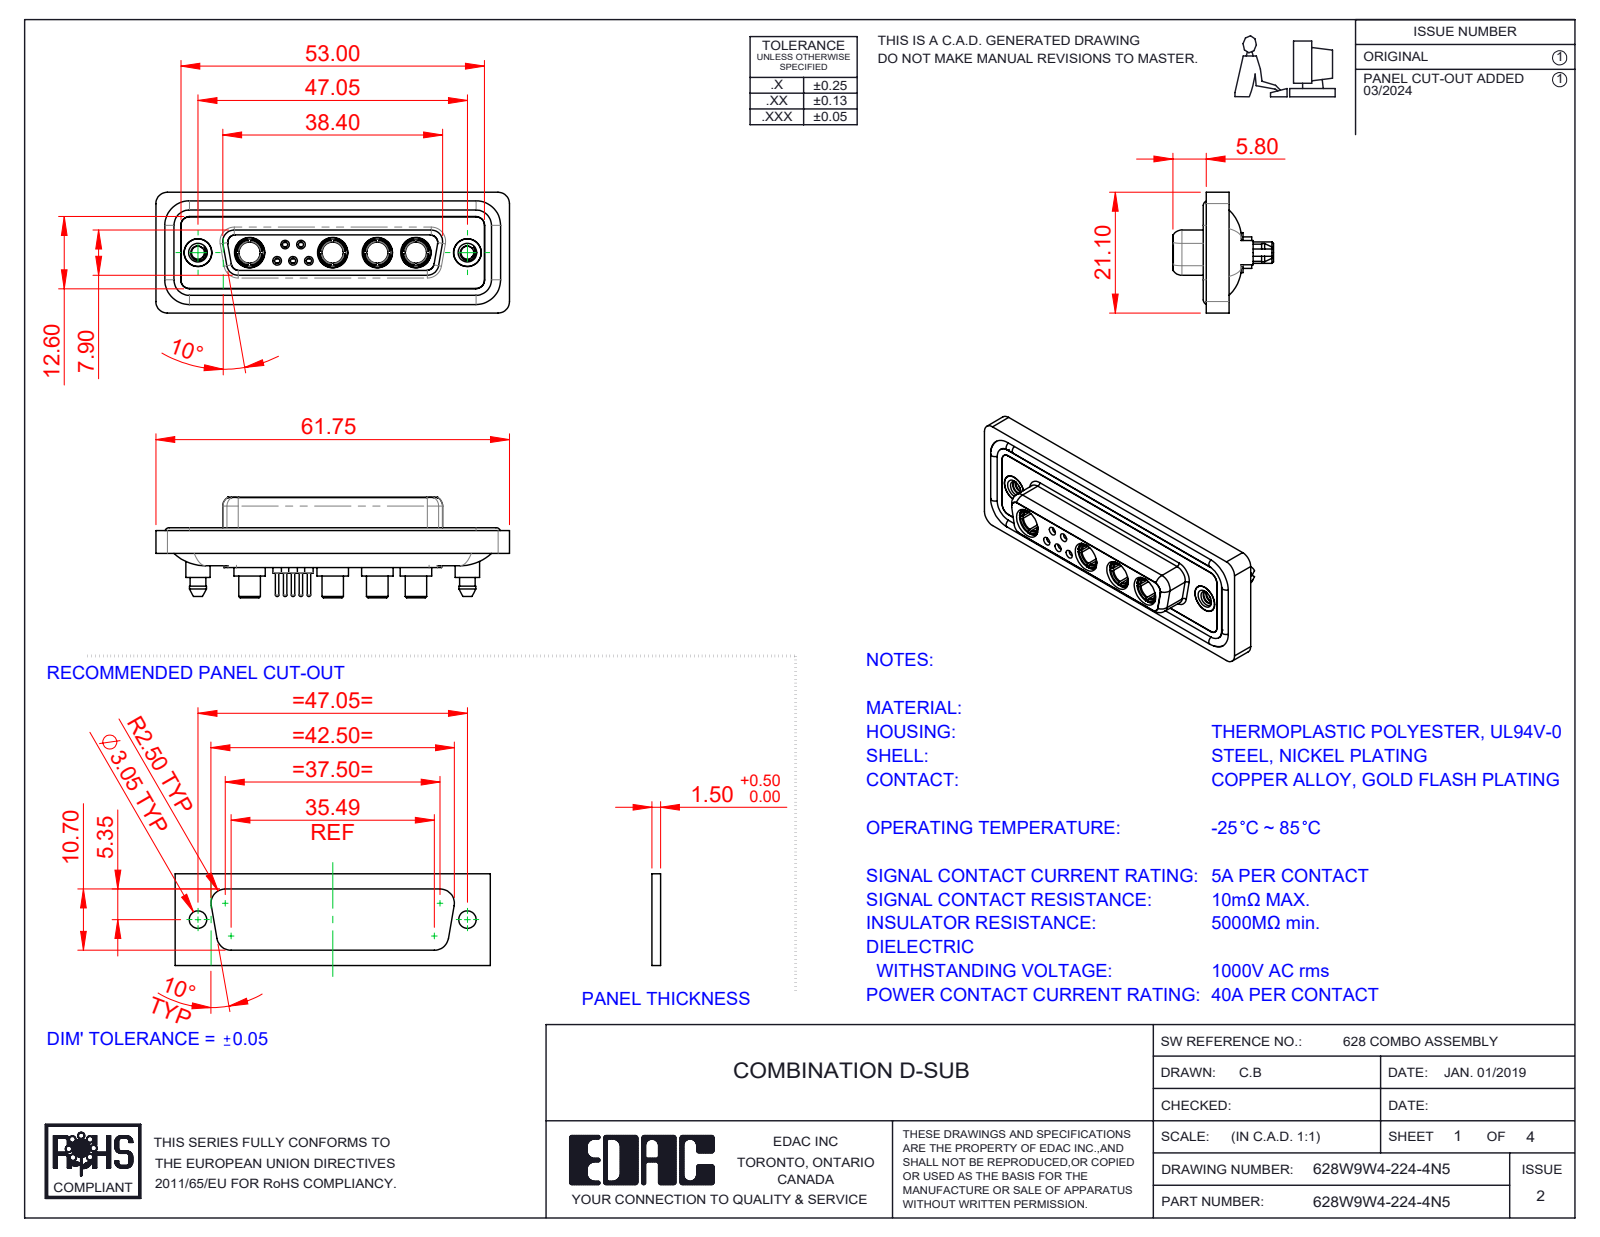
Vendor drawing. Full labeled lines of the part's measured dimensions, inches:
Part name (STEP PRODUCT): Power Socket_40A S; 628Combo Housing_9W4; 628Combo Shell Front_25 Contacts; 628Combo Contact Row 2_24 (+5 more)
STEP written by: SolidWorks 2023 (CONFIG_CONTROL_DESIGN)
Units: inches
Bodies: 20 solids, 1007 faces (312 planar, 407 cylindrical, 288 other)
Overall size (bounding box): 2.431 × 0.831 × 0.691
Volume: 0.514 in³ · Surface area: 21.61 in²
Round holes (diameter × count): ⌀0.191 ×6, ⌀0.035 ×5, ⌀0.043 ×5, ⌀0.059 ×5, ⌀0.079 ×5, ⌀0.146 ×4, ⌀0.209 ×4, ⌀0.063 ×3, ⌀0.067 ×2, ⌀0.089 ×2, ⌀0.157 ×2, ⌀0.159 ×2
Round bosses / shafts (diameter × count): ⌀0.063 ×6, ⌀0.087 ×5, ⌀0.024 ×5, ⌀0.217 ×4, ⌀0.205 ×4, ⌀0.195 ×4, ⌀0.187 ×4, ⌀0.148 ×4
Partial cylindrical surfaces — rounded edges, fillets, slot ends (radius × count): R0.059 ×24, R0.079 ×18, R0.063 ×10, R0.053 ×8, R0.01 ×4, R0.02 ×4, R0.024 ×4, R0.026 ×4
Main face-to-face distances: 0.016, 0.071, 0.293, 0.222, 0.02, 0.278, 0.26, 0.063, 0.043, 0.114
Hole centre spacings: 0.124, 0.109, 0.198, 0.109, 0.173, 0.198, 0.218, 0.226
